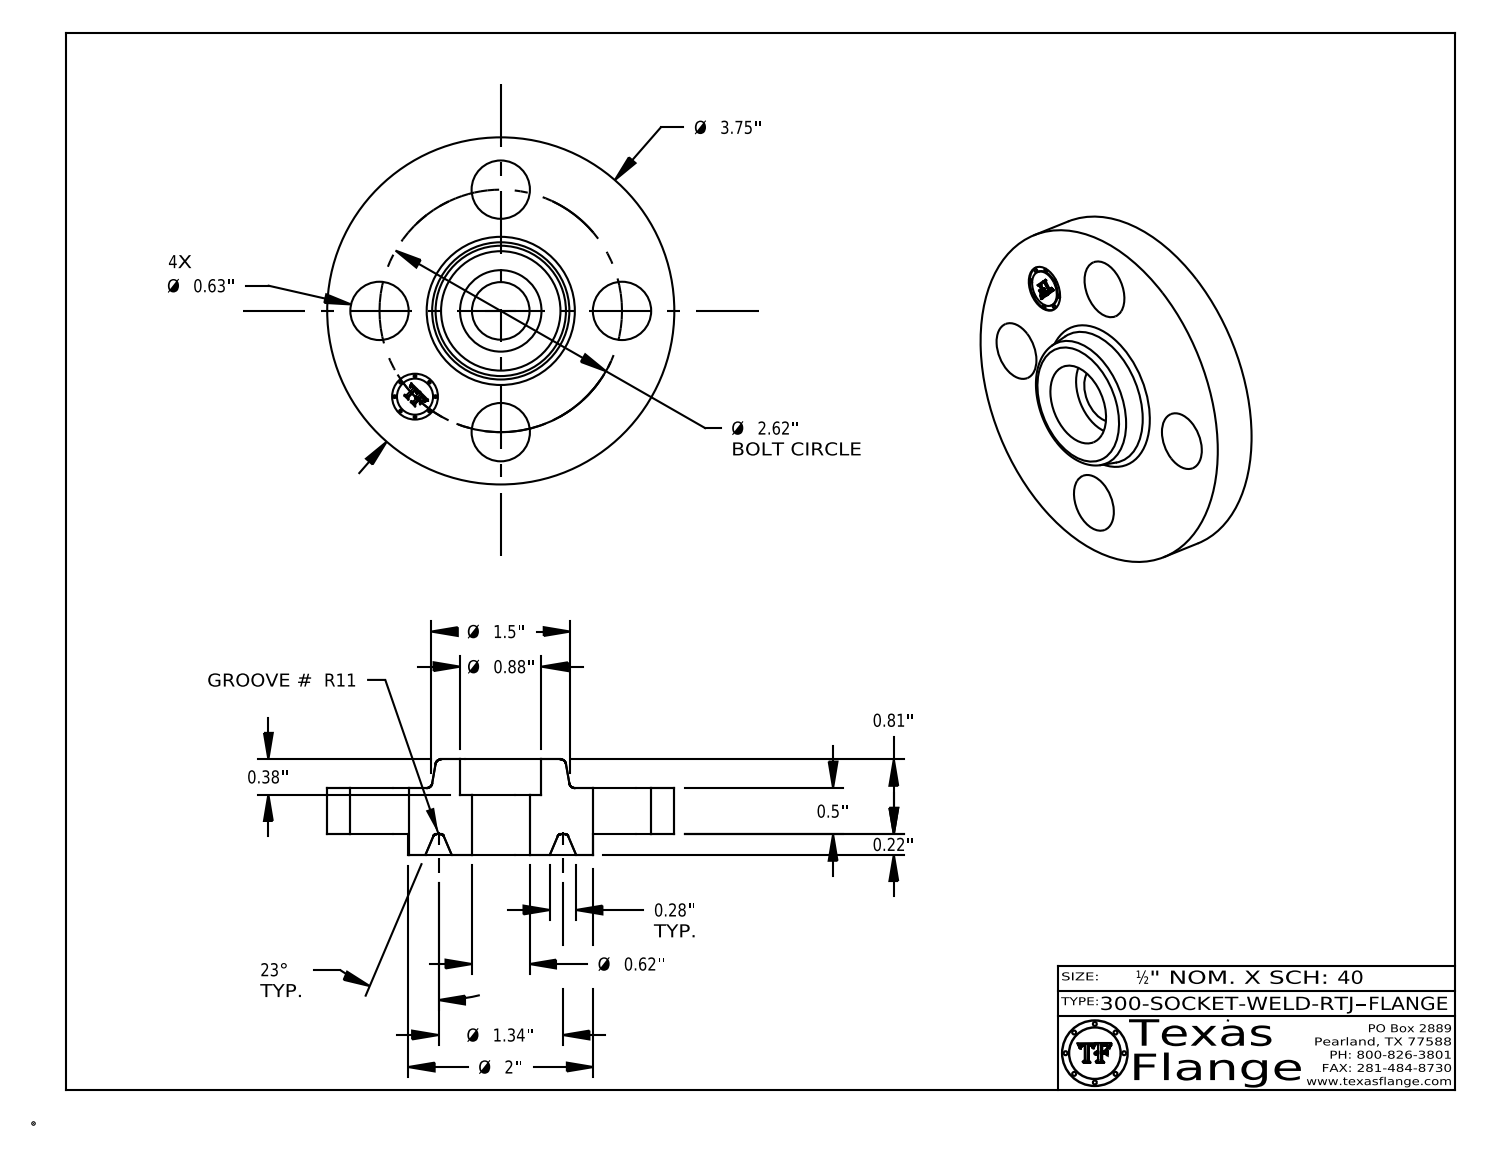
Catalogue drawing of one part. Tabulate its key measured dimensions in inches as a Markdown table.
| quantity | value |
| --- | --- |
| part name | 300-SOCKET-WELD-RTJ |
| STEP written by | CATIA V5 STEP AP214 (AUTOMOTIVE_DESIGN) |
| units | inches |
| bodies | 1 solid, 426 faces (372 planar, 40 cylindrical, 14 other) |
| overall size | 3.75 × 3.75 × 1.029 |
| volume | 5.493 in³ |
| surface area | 34.84 in² |
| round holes (diameter × count) | 0.63 × 4, 0.495 × 1, 0.622 × 1, 0.88 × 1 |
| round bosses / shafts (diameter × count) | 0.03 × 8, 3.75 × 1, 2 × 1, 0.39 × 1 |
| main face-to-face distances | 0.5, 0.219, 0.719, 1.029, 0.81, 0.31, 0.07, 0.649, 0.43, 0.38 |
| hole center spacings | 1.31, 1.852, 1.003, 2.42, 2.62, 1.31 |
